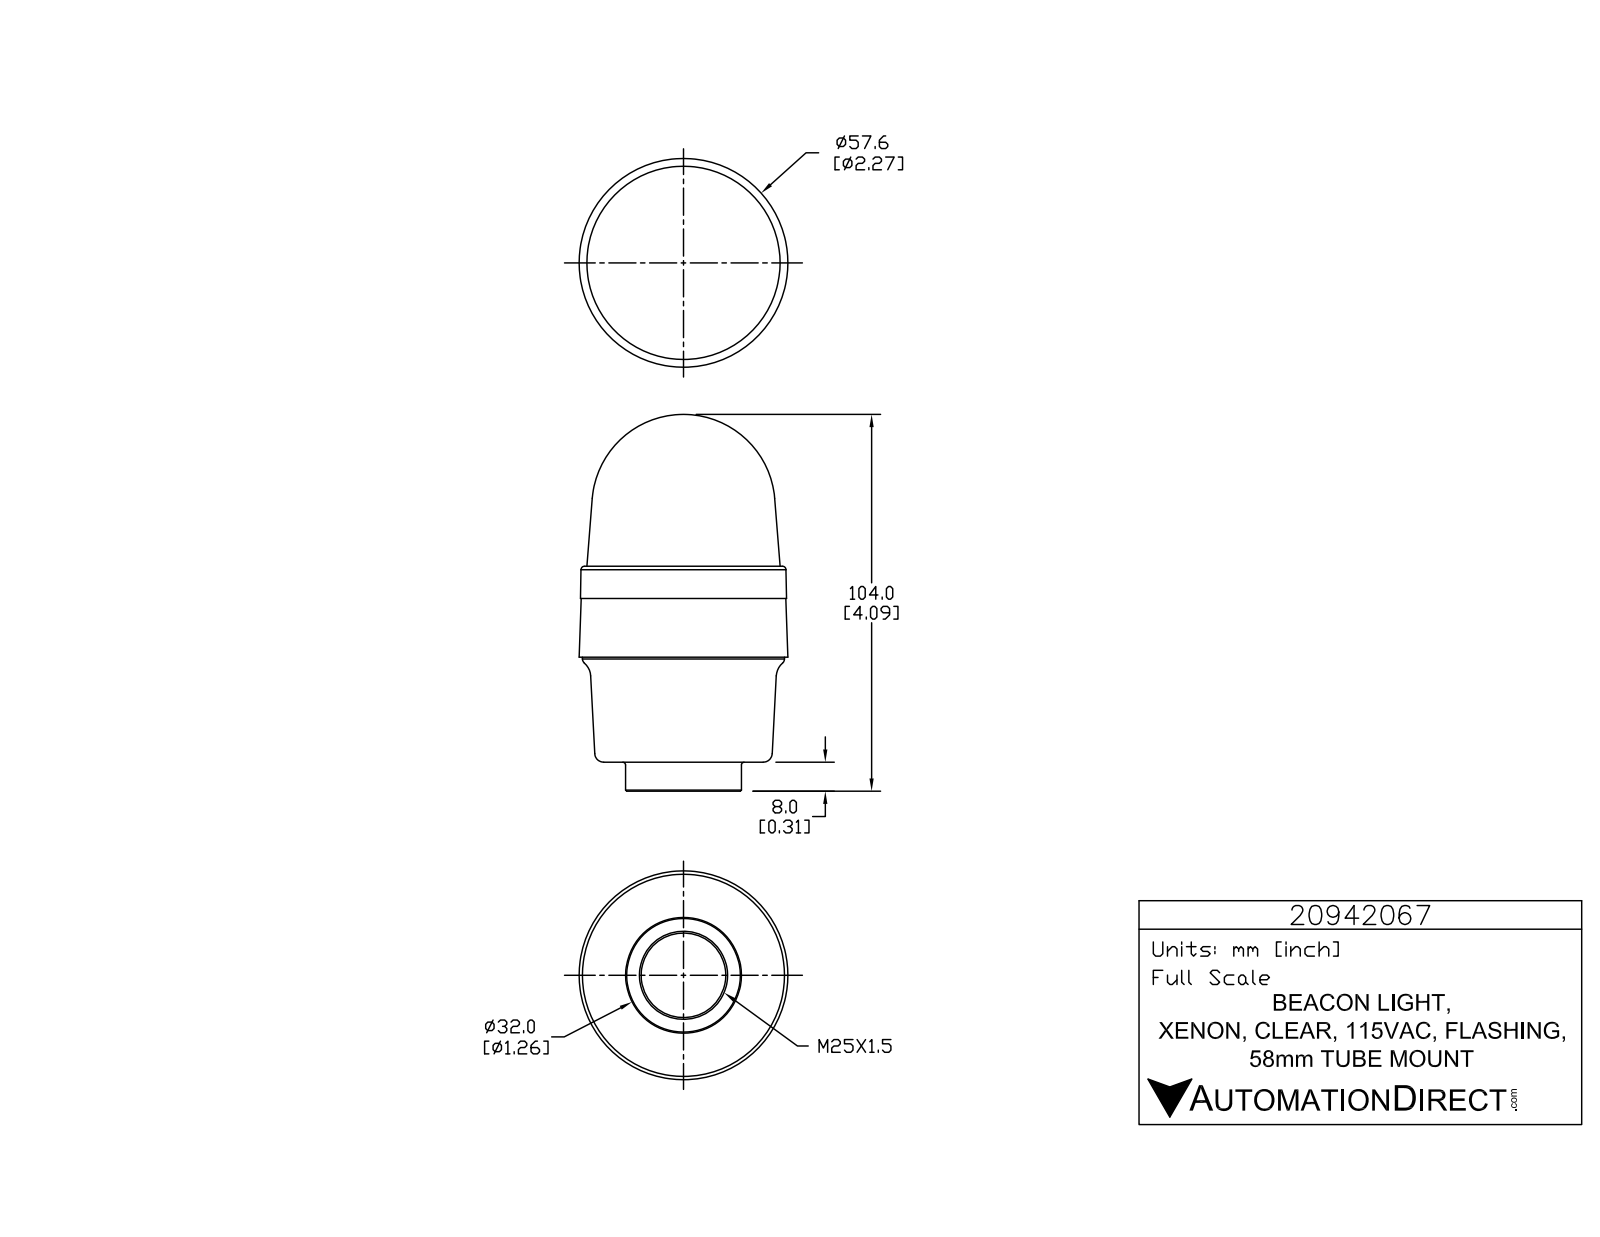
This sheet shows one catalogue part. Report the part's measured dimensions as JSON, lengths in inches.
{"part_name": "20942067", "step_written_by": "SolidWorks 2015 (AUTOMOTIVE_DESIGN)", "units": "inches", "bodies": {"solids": 1, "faces": 791, "planar": 525, "cylindrical": 168, "other": 98}, "overall_size": [4.051, 2.269, 2.269], "volume_in3": 11.72, "surface_area_in2": 29.93, "round_holes": [[0.039, 3], [0.92, 1]], "round_bosses_or_shafts": [[0.226, 3], [0.056, 3], [2.197, 1], [1.26, 1]], "partial_cylinders_radius": [[0.008, 6], [0.008, 6], [0.008, 6], [0.131, 6], [0.004, 3], [0.005, 3], [0.008, 3], [0.008, 3]], "face_to_face_distances": [0.315, 1.142, 1.457, 0.988, 2.13, 2.445, 0.35, 0.638, 1.78, 2.094]}
